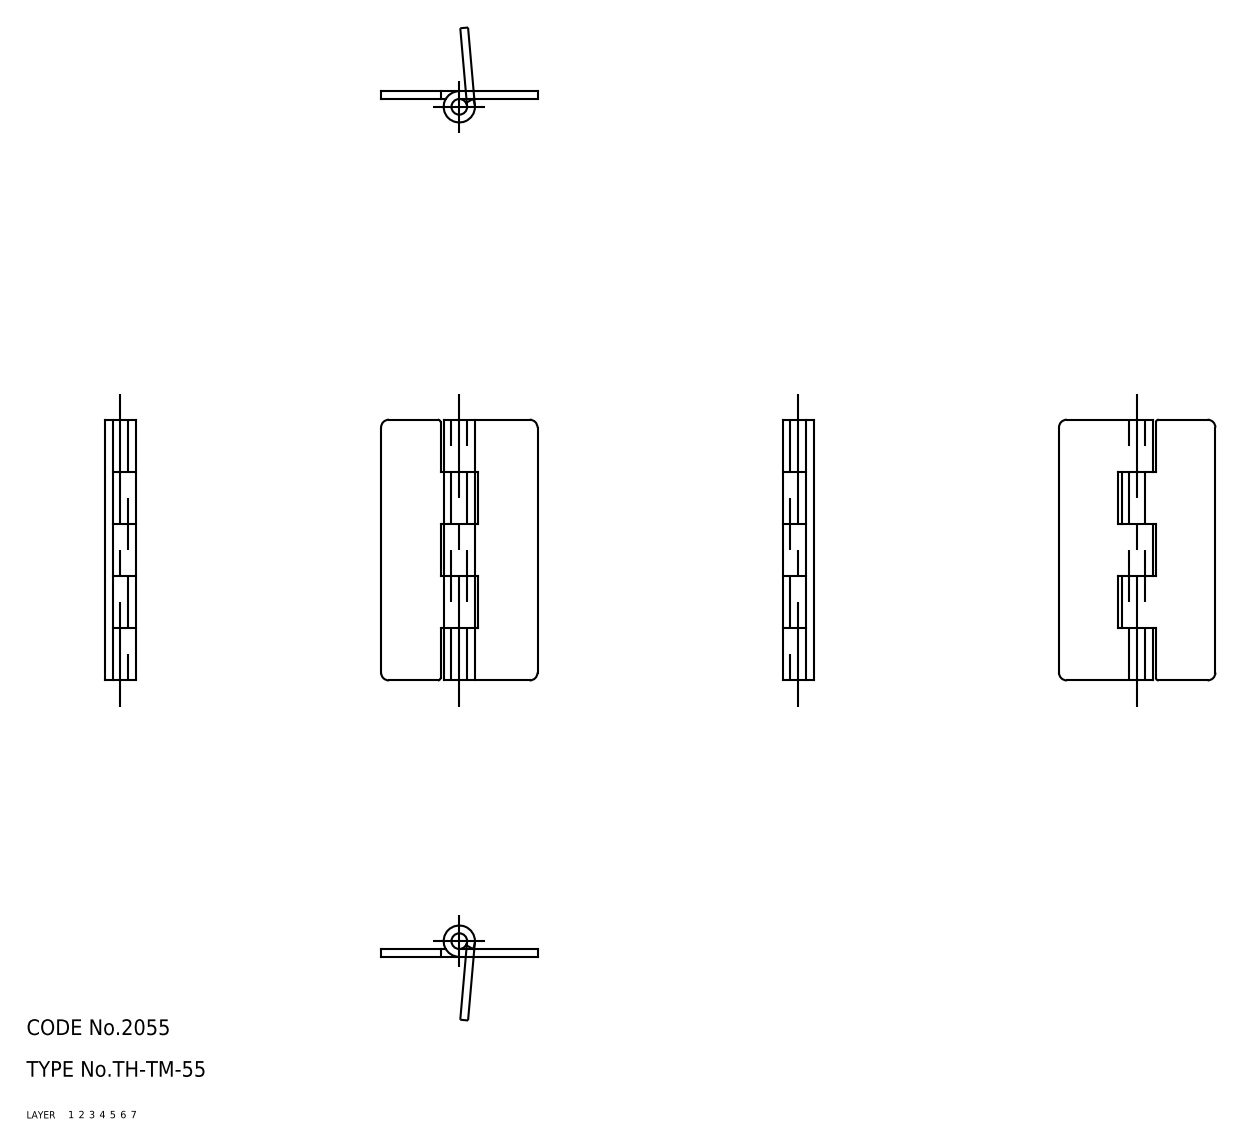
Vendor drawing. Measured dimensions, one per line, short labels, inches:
name: hinge piece_B; hinge piece_A; shaft; TH_TM_55_24159_36
written by: CADfix (AUTOMOTIVE_DESIGN)
unit: in
bodies: 3 solids, 48 faces (0 planar, 0 cylindrical, 48 other)
size: 1.969 × 1.181 × 0.236
volume: 0.196 in³; area: 7.58 in²
